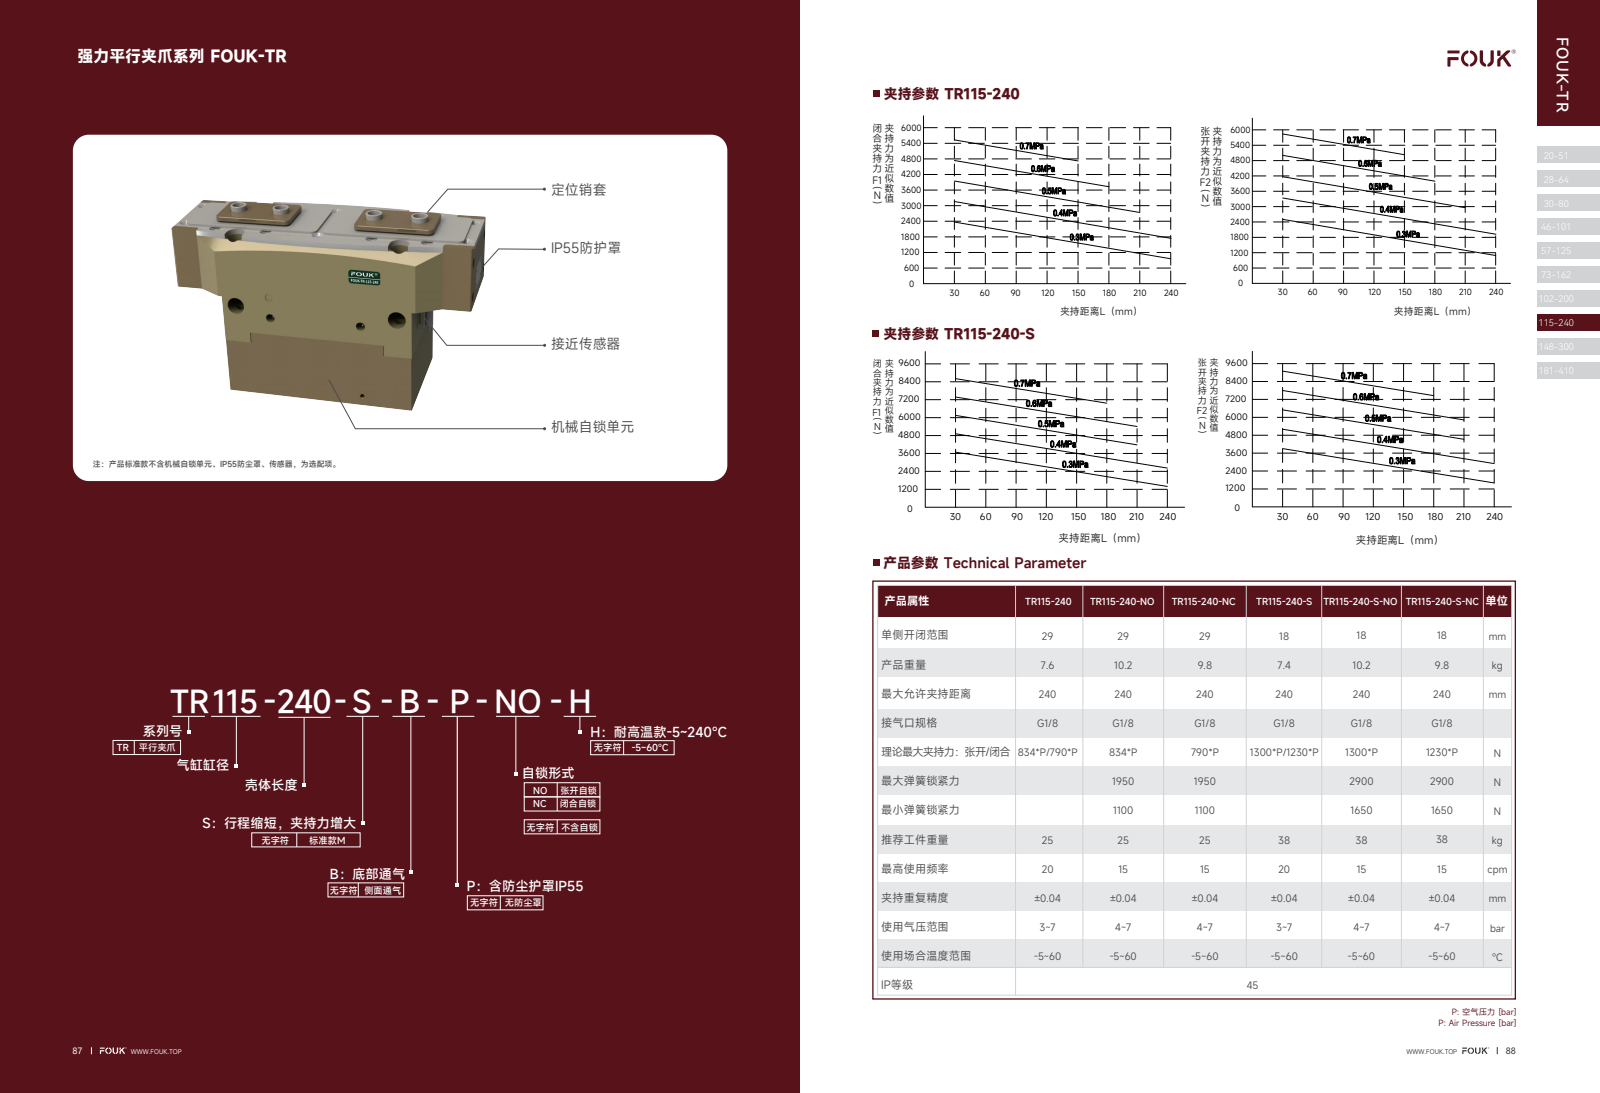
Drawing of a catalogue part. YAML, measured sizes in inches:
part_name: "TR115-240-S; 30x14-R3"
step_written_by: "SolidWorks 2018 (CONFIG_CONTROL_DESIGN)"
units: inches
bodies: {solids: 21, faces: 1266, planar: 580, cylindrical: 364, other: 322}
overall_size: [9.449, 4.449, 4.331]
volume: 140.5
surface_area: 430.8
round_holes:
  - {diameter: 0.165, count: 18}
  - {diameter: 0.402, count: 10}
  - {diameter: 0.13, count: 6}
  - {diameter: 0.63, count: 6}
  - {diameter: 0.669, count: 6}
  - {diameter: 0.106, count: 4}
  - {diameter: 0.177, count: 4}
  - {diameter: 0.315, count: 4}
  - {diameter: 0.472, count: 4}
  - {diameter: 0.118, count: 3}
  - {diameter: 0.323, count: 3}
  - {diameter: 0.081, count: 2}
round_bosses_or_shafts:
  - {diameter: 0.63, count: 3}
  - {diameter: 0.315, count: 2}
  - {diameter: 0.15, count: 2}
  - {diameter: 0.098, count: 2}
  - {diameter: 0.079, count: 2}
  - {diameter: 0.146, count: 1}
  - {diameter: 0.071, count: 1}
partial_cylinders:
  - {radius: 0.005, count: 18}
  - {radius: 0.005, count: 12}
  - {radius: 0.118, count: 8}
  - {radius: 0.059, count: 6}
  - {radius: 0.02, count: 4}
  - {radius: 0.197, count: 4}
  - {radius: 0.976, count: 4}
  - {radius: 0.984, count: 4}
face_to_face_distances: [2.165, 1.063, 1.535, 3.268, 3.701, 4.331, 0.425, 2.591, 4.126, 2.205]
hole_center_spacings: [2.047, 3.308, 1.307, 4.094, 4.849, 2.598, 0.167, 0.669]
